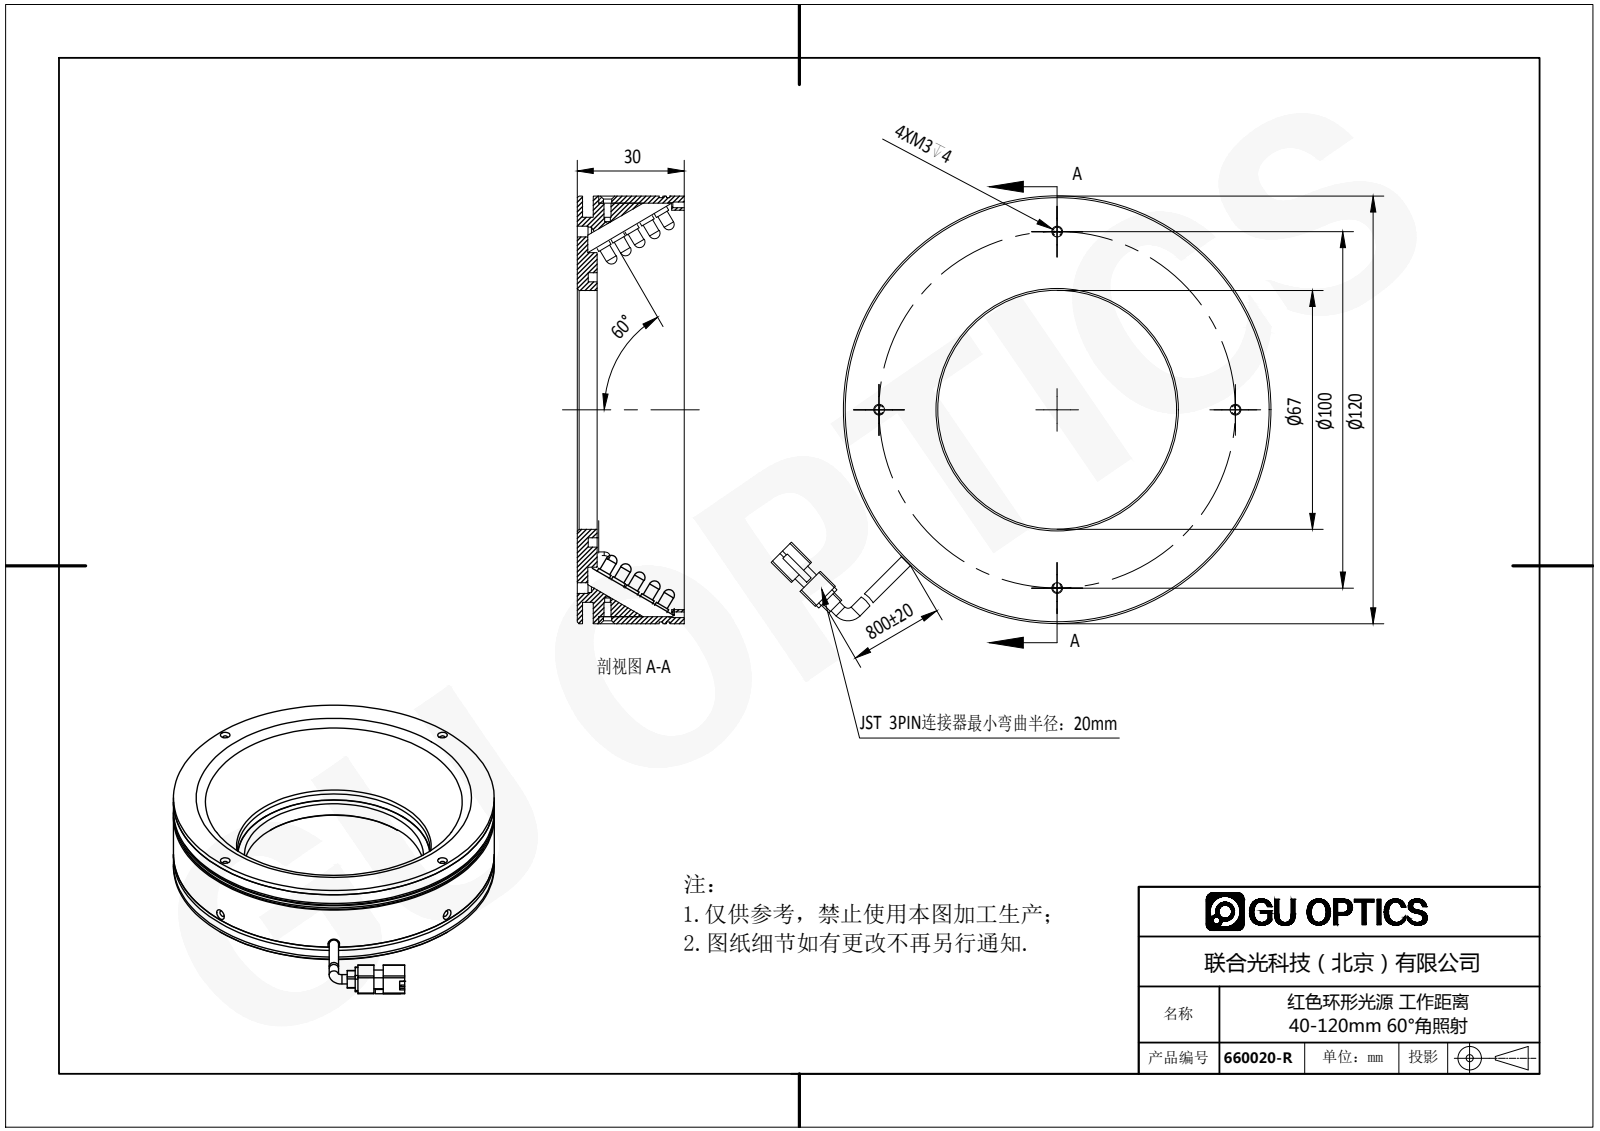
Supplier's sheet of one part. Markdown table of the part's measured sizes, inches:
| quantity | value |
| --- | --- |
| part name | 660020-R |
| STEP written by | SolidWorks 2016 (AUTOMOTIVE_DESIGN) |
| units | inches |
| bodies | 356 solids, 6266 faces (4293 planar, 1552 cylindrical, 421 other) |
| overall size | 5.522 × 4.724 × 1.26 |
| volume | 6.578 in³ |
| surface area | 193.5 in² |
| round holes (diameter × count) | 0.063 × 6, 0.138 × 5, 0.049 × 4, 0.067 × 4, 0.118 × 4, 0.079 × 2, 0.091 × 2, 2.638 × 1, 2.835 × 1, 3.031 × 1, 4.409 × 1 |
| round bosses / shafts (diameter × count) | 0.15 × 350, 0.118 × 350, 0.138 × 2, 4.724 × 1, 4.685 × 1, 4.567 × 1, 4.252 × 1, 3.472 × 1 |
| partial cylindrical surfaces (radius × count) | 0.02 × 8, 0.039 × 4, 0.049 × 4, 0.065 × 1, 0.394 × 1 |
| main face-to-face distances | 1.181, 0.059, 0.177, 0.079, 0.118, 1.26, 1.004, 1.122, 1.201, 1.083 |
| hole center spacings | 3, 0.295, 1.969, 2.264, 2.784, 3.202, 4.232, 3.937 |
